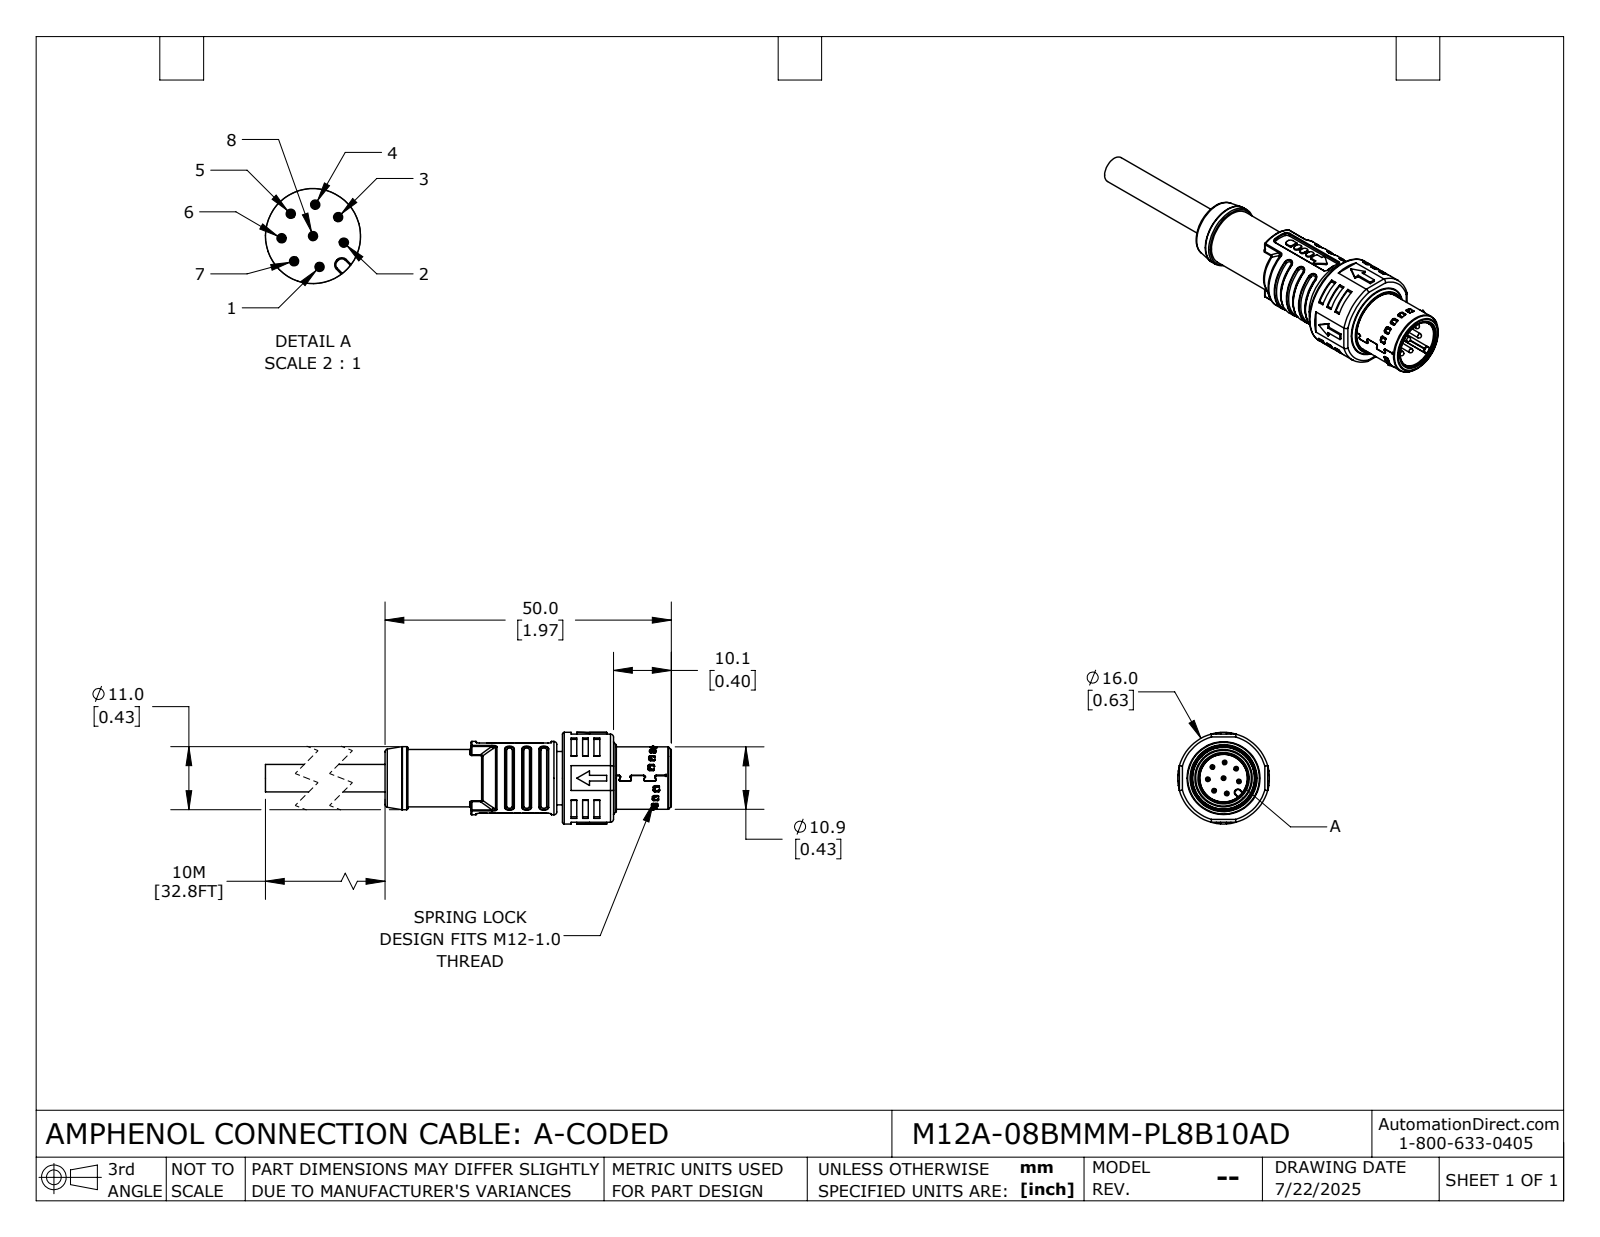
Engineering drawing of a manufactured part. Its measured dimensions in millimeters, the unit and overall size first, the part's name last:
Units: millimetres
Overall size (bounding box): 75 × 16 × 16
Round holes (diameter × count): ⌀8.3 ×1, ⌀9 ×1, ⌀10.15 ×1, ⌀10.5 ×1, ⌀10.9 ×1, ⌀11.5 ×1, ⌀11.8 ×1, ⌀14.2 ×1
Round bosses / shafts (diameter × count): ⌀0.8 ×8, ⌀16 ×1, ⌀14.1 ×1, ⌀12.8 ×1, ⌀12.4 ×1, ⌀11 ×1, ⌀10.45 ×1, ⌀10.4 ×1
Partial cylindrical surfaces — rounded edges, fillets, slot ends (radius × count): R0.2 ×114, R0.25 ×66, R0.3 ×64, R0.15 ×44, R0.5 ×38, R0.13 ×12, R0.7 ×11, R0.1 ×10
Main face-to-face distances: 1, 10.1, 8.6, 8.9, 2.5, 1.5, 1.2, 32.5, 15.4, 41.1
Volume: 5 223 mm³ · Surface area: 5 723 mm²
Bodies: 1 solid, 2027 faces (880 planar, 644 cylindrical, 503 other)
Part name (STEP PRODUCT): M12A-08BMMM-PL8B10AD
STEP written by: SolidWorks 2024 (CONFIG_CONTROL_DESIGN)
